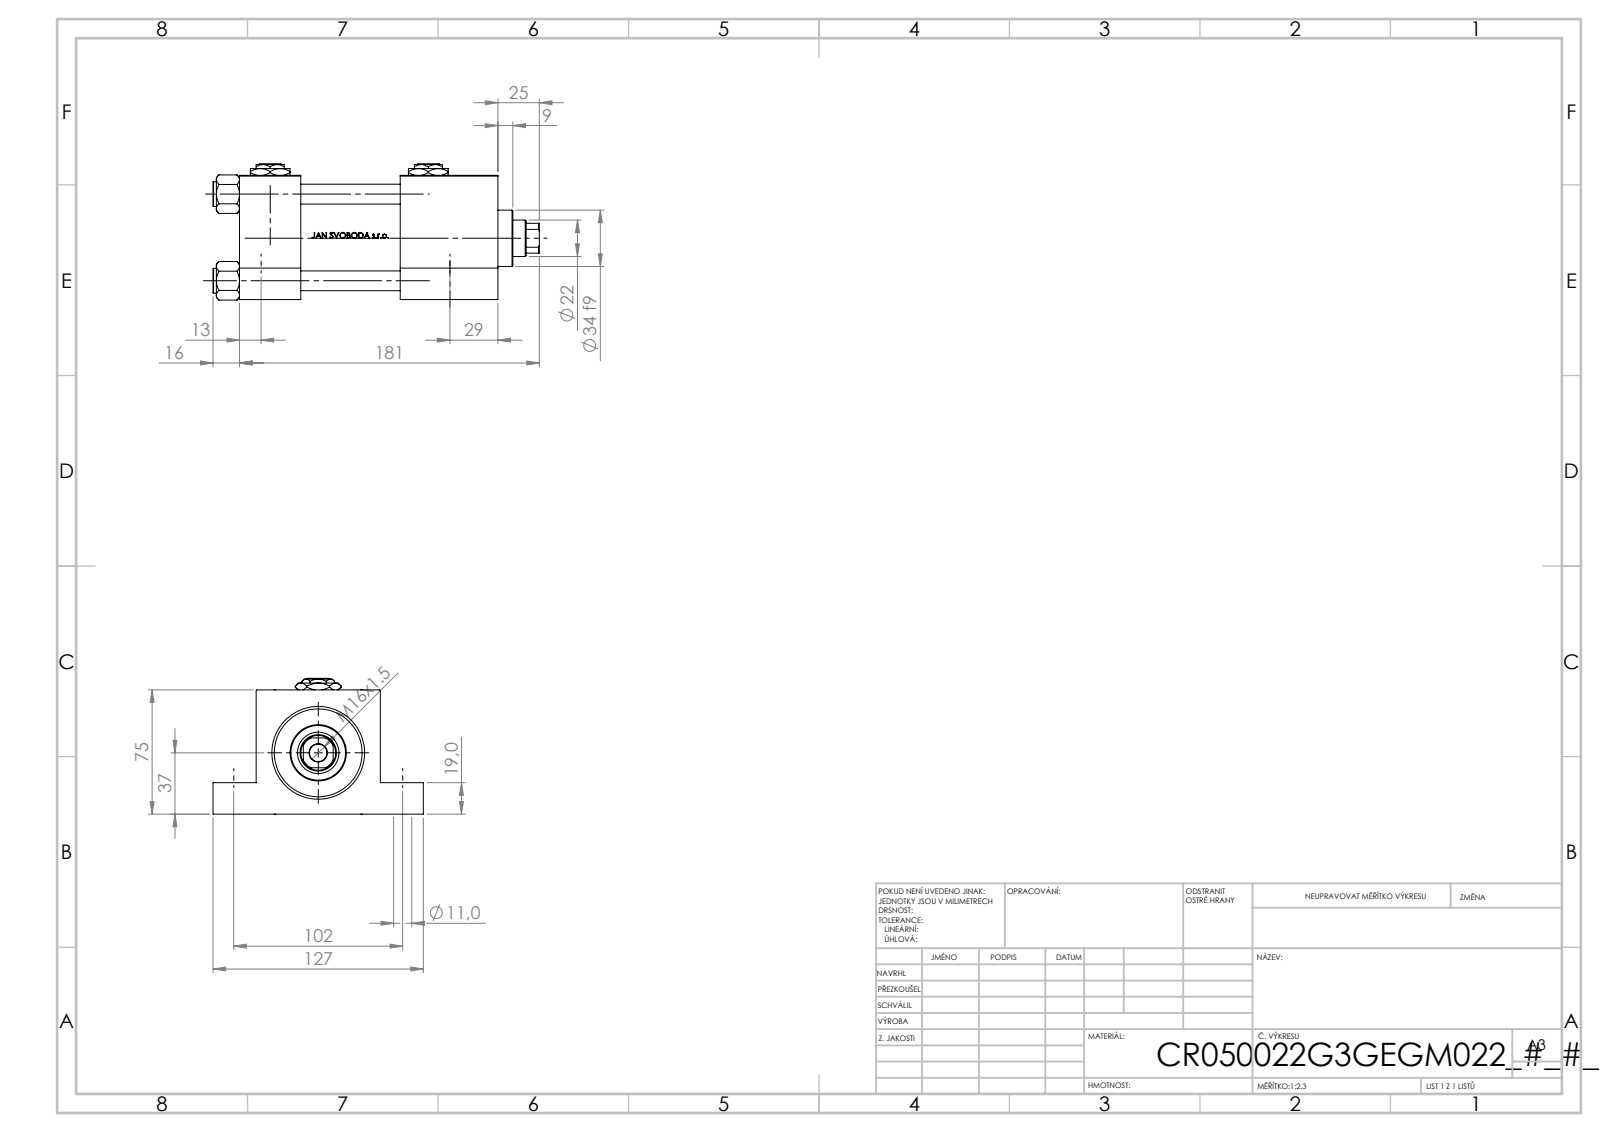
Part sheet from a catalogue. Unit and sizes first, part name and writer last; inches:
Units: inches
Overall size (bounding box): 7.756 × 5 × 3.239
Round holes (diameter × count): ⌀0.472 ×4, ⌀0.551 ×4, ⌀0.276 ×2, ⌀0.825 ×2, ⌀1.181 ×2, ⌀0.413 ×1, ⌀0.866 ×1, ⌀0.984 ×1, ⌀1.614 ×1, ⌀1.969 ×1, ⌀2.087 ×1
Round bosses / shafts (diameter × count): ⌀0.591 ×4, ⌀2.205 ×1, ⌀1.339 ×1
Partial cylindrical surfaces — rounded edges, fillets, slot ends (radius × count): R0.413 ×1
Main face-to-face distances: 2.953, 1.457, 6.142, 4.685, 0.748, 3.819, 2.205, 2.362, 2.323, 1.024
Hole centre spacings: 1.456, 2.059, 2.02, 2.072, 2.912, 4.016, 4.455, 4.488
Volume: 48.51 in³ · Surface area: 275.3 in²
Bodies: 17 solids, 1252 faces (496 planar, 136 cylindrical, 620 other)
Part name (STEP PRODUCT): V215CR_G_Body; NUT_M5_G; V215CR_G_TYCINKA; V215_VC_A (+2 more)
STEP written by: SolidWorks 2019 (CONFIG_CONTROL_DESIGN)
